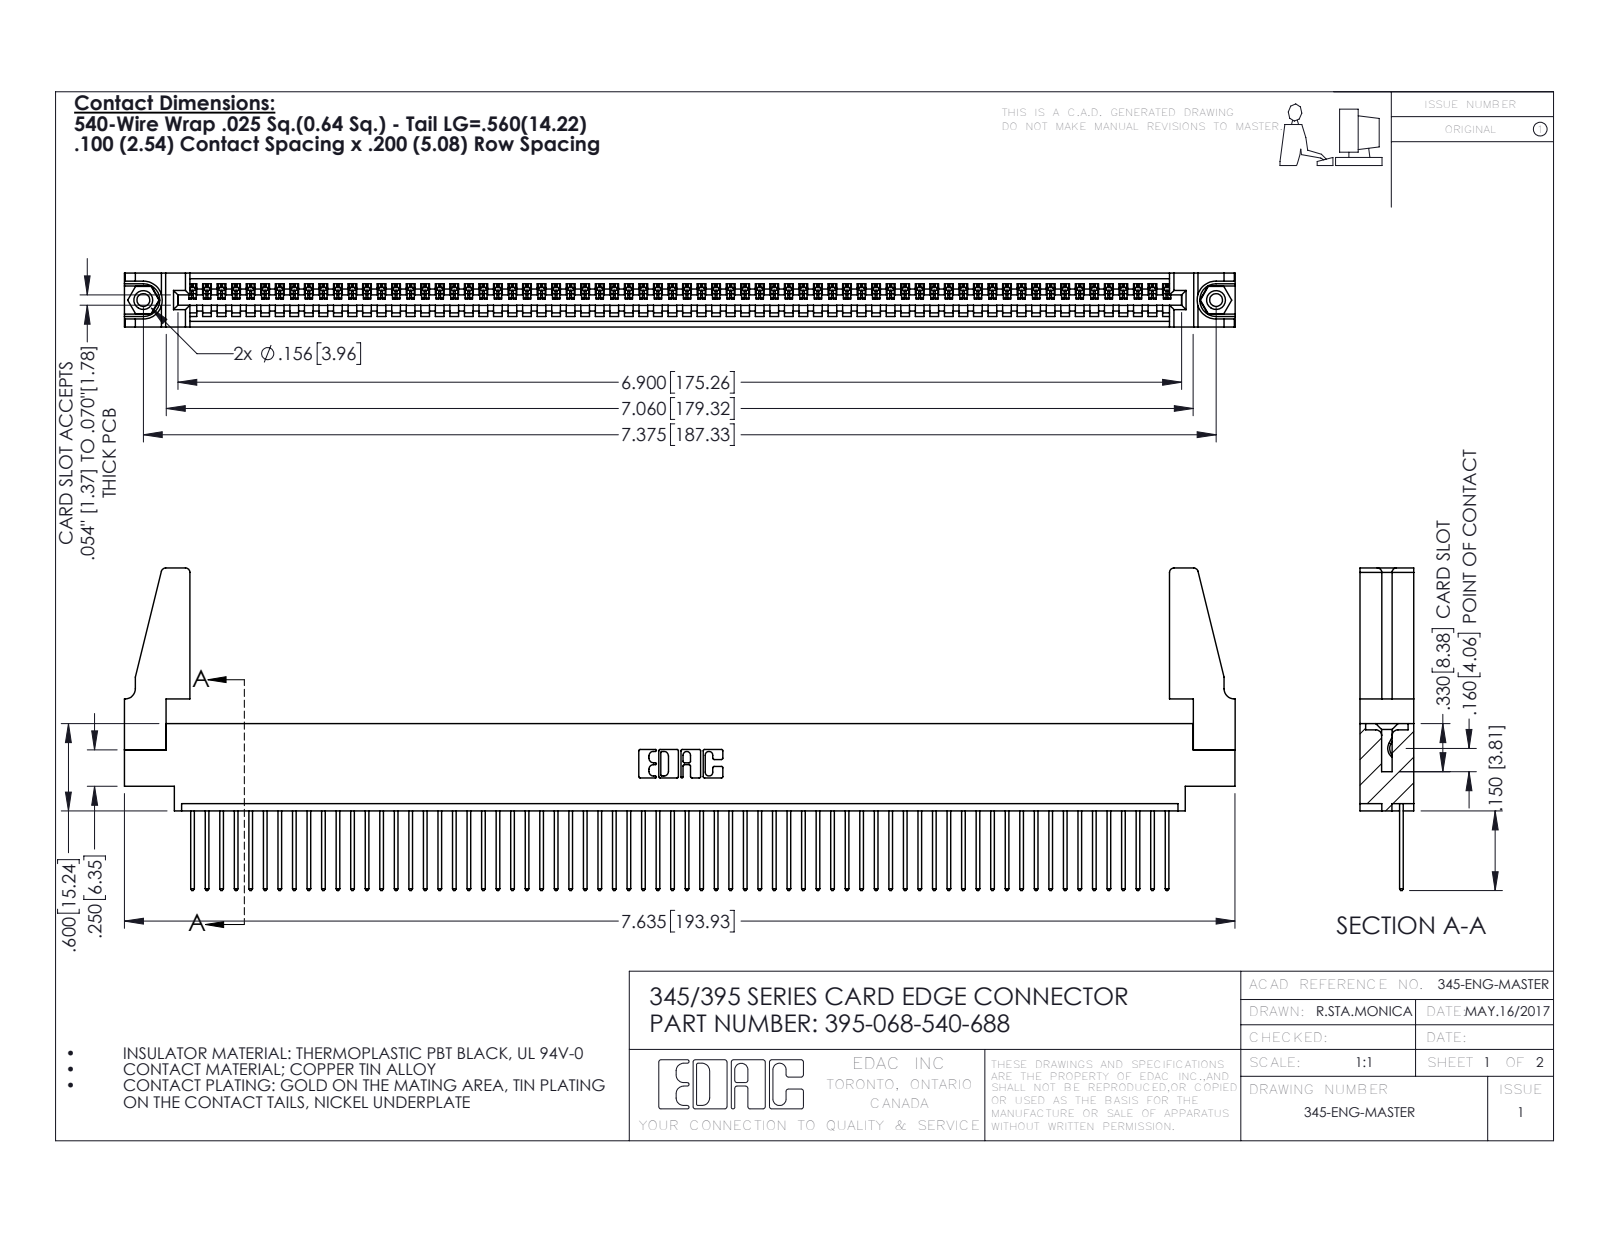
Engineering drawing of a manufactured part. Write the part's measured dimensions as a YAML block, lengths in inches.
part_name: "345-292-001_345-293-140; 345-220-078_345-220-088; 345 Part_0.170 Offset - 0.156 Dia-TH; 395-068-540-688 (+1 more)"
step_written_by: "SolidWorks 2016 (CONFIG_CONTROL_DESIGN)"
units: inches
bodies: {solids: 73, faces: 4198, planar: 2876, cylindrical: 1306, other: 16}
overall_size: [7.636, 2.217, 0.37]
volume: 1.334
surface_area: 44.96
round_holes:
  - {diameter: 0.089, count: 2}
  - {diameter: 0.125, count: 2}
  - {diameter: 0.156, count: 2}
  - {diameter: 0.064, count: 1}
round_bosses_or_shafts:
  - {diameter: 0.155, count: 2}
partial_cylinders:
  - {radius: 0.006, count: 136}
  - {radius: 0.01, count: 136}
  - {radius: 0.01, count: 22}
  - {radius: 0.03, count: 8}
  - {radius: 0.007, count: 6}
  - {radius: 0.031, count: 6}
  - {radius: 0.026, count: 3}
  - {radius: 0.031, count: 2}
face_to_face_distances: [0.072, 0.298, 0.37, 0.098, 0.272, 0.025, 0.2, 0.225, 0.175, 0.149]
hole_center_spacings: [0.27, 7.139, 7.375]
